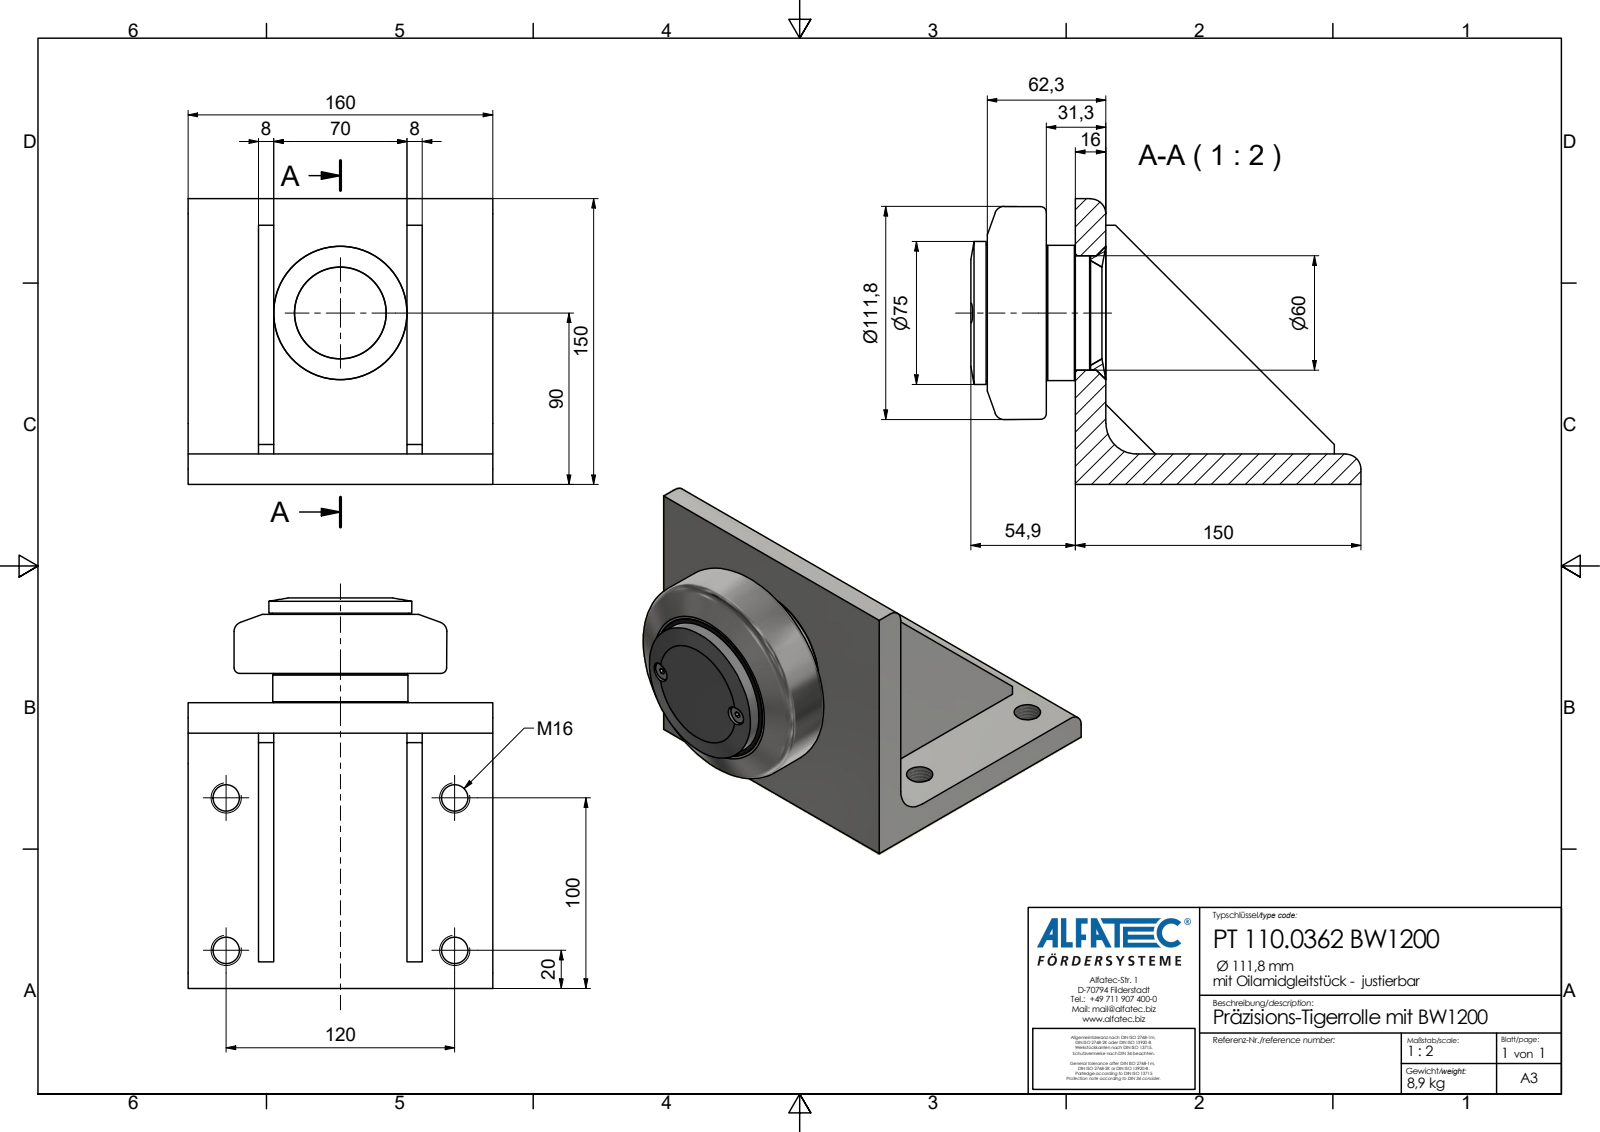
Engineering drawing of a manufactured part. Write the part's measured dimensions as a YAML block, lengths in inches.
part_name: "PT 110.0362 BW1200_Kontur"
step_written_by: "Autodesk Inventor 2020 (AP242_MANAGED_MODEL_BASED_3D_ENGINEERING_MIM_LF)"
units: inches
bodies: {solids: 1, faces: 65, planar: 41, cylindrical: 15, other: 9}
overall_size: [8.067, 6.299, 5.906]
volume: 74.88
surface_area: 249.9
round_holes:
  - {diameter: 0.545, count: 4}
  - {diameter: 0.409, count: 2}
round_bosses_or_shafts:
  - {diameter: 0.384, count: 2}
  - {diameter: 2.953, count: 1}
  - {diameter: 2.819, count: 1}
  - {diameter: 2.795, count: 1}
  - {diameter: 2.776, count: 1}
partial_cylinders:
  - {radius: 0.315, count: 2}
  - {radius: 0.63, count: 1}
face_to_face_distances: [0.63, 0.315, 3.071, 1.457, 1.772, 4.528, 4.843, 3.386, 2.756, 1.232]
hole_center_spacings: [3.15, 4.724, 5.678, 2.205]
